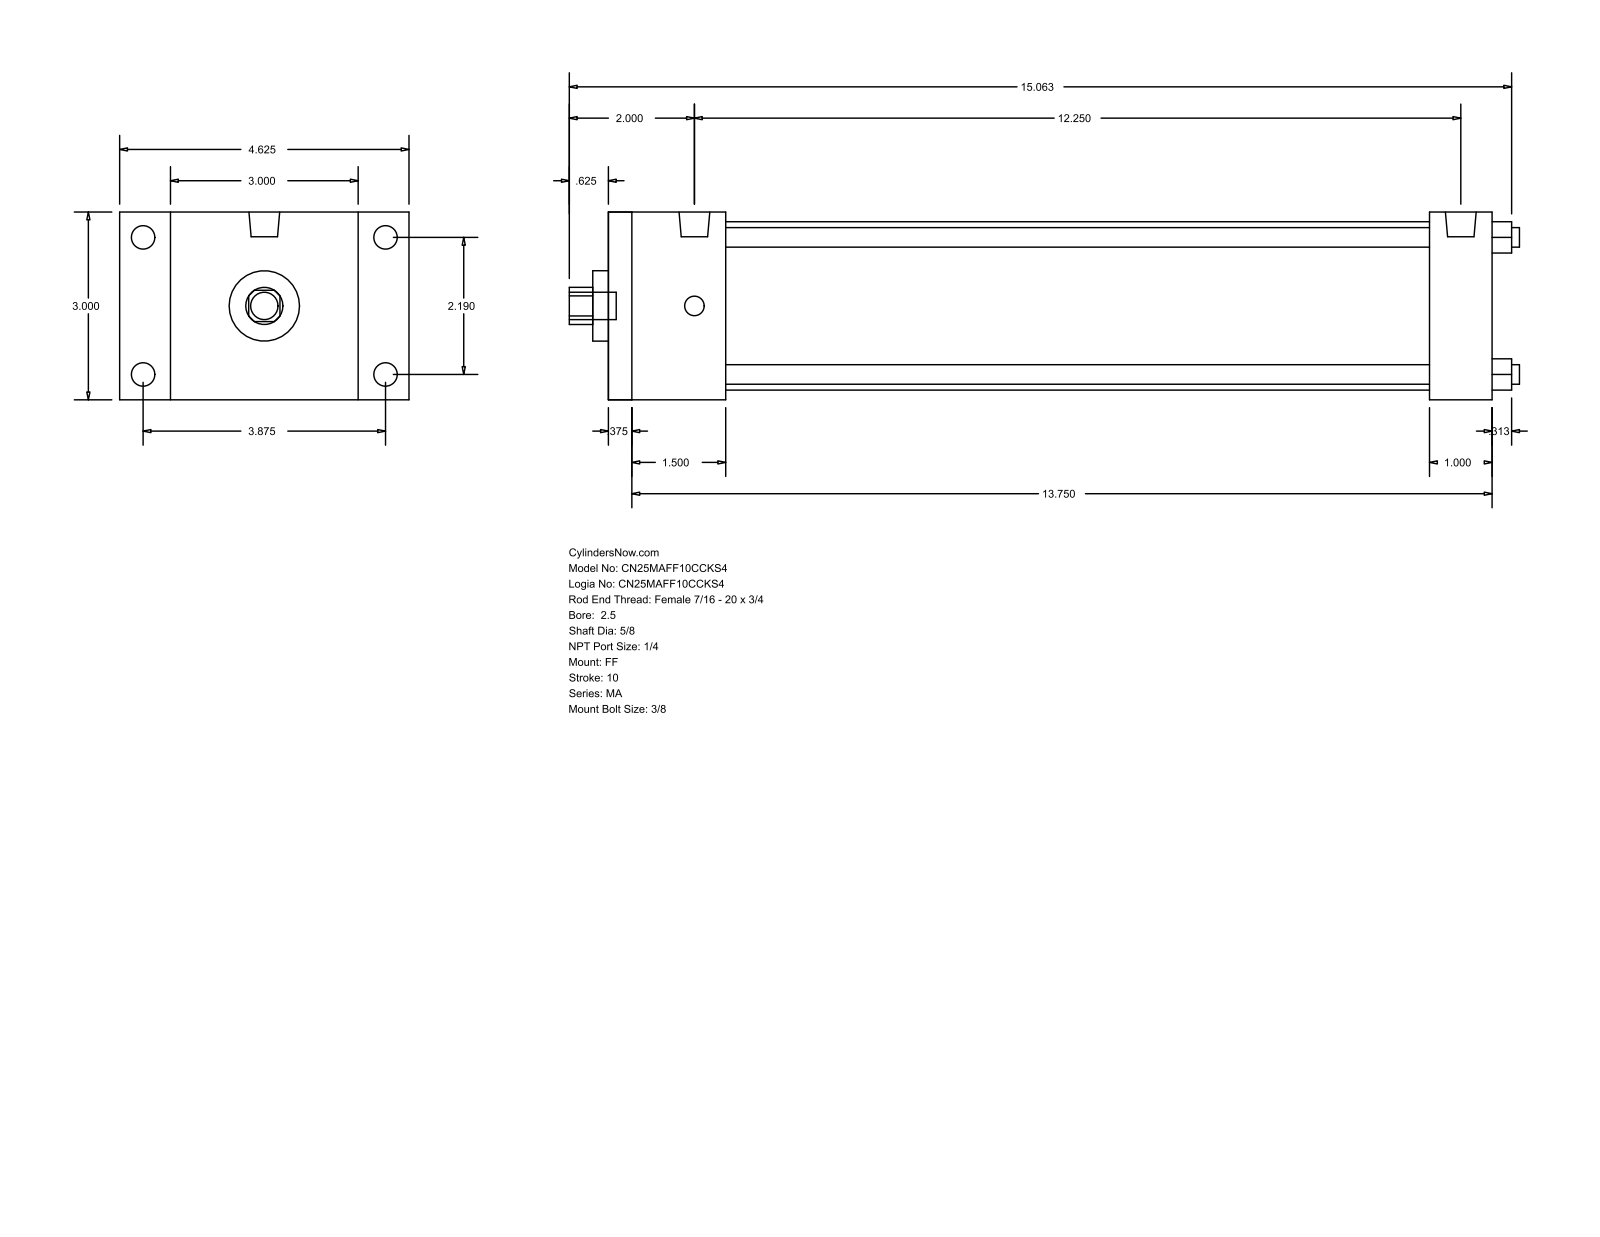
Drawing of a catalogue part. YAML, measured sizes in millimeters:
part_name: "MA_FF__0250_0.625"
step_written_by: "GSSL Pune (CONFIG_CONTROL_DESIGN)"
units: millimeters
bodies: {solids: 0, faces: 92, planar: 64, cylindrical: 28, other: 0}
overall_size: [385.76, 117.47, 76.2]
round_holes:
  - {diameter: 7.94, count: 4}
  - {diameter: 15.88, count: 1}
  - {diameter: 28.57, count: 1}
  - {diameter: 68.33, count: 1}
round_bosses_or_shafts:
  - {diameter: 9.53, count: 4}
  - {diameter: 7.94, count: 4}
  - {diameter: 12.49, count: 2}
  - {diameter: 11.11, count: 1}
partial_cylinders:
  - {radius: 7.54, count: 1}
face_to_face_distances: [76.2, 358.77, 9.52, 349.25, 25.4, 47.62, 333.37, 38.1, 323.85, 285.75]
hole_center_spacings: [39.33, 55.62, 78.66]
